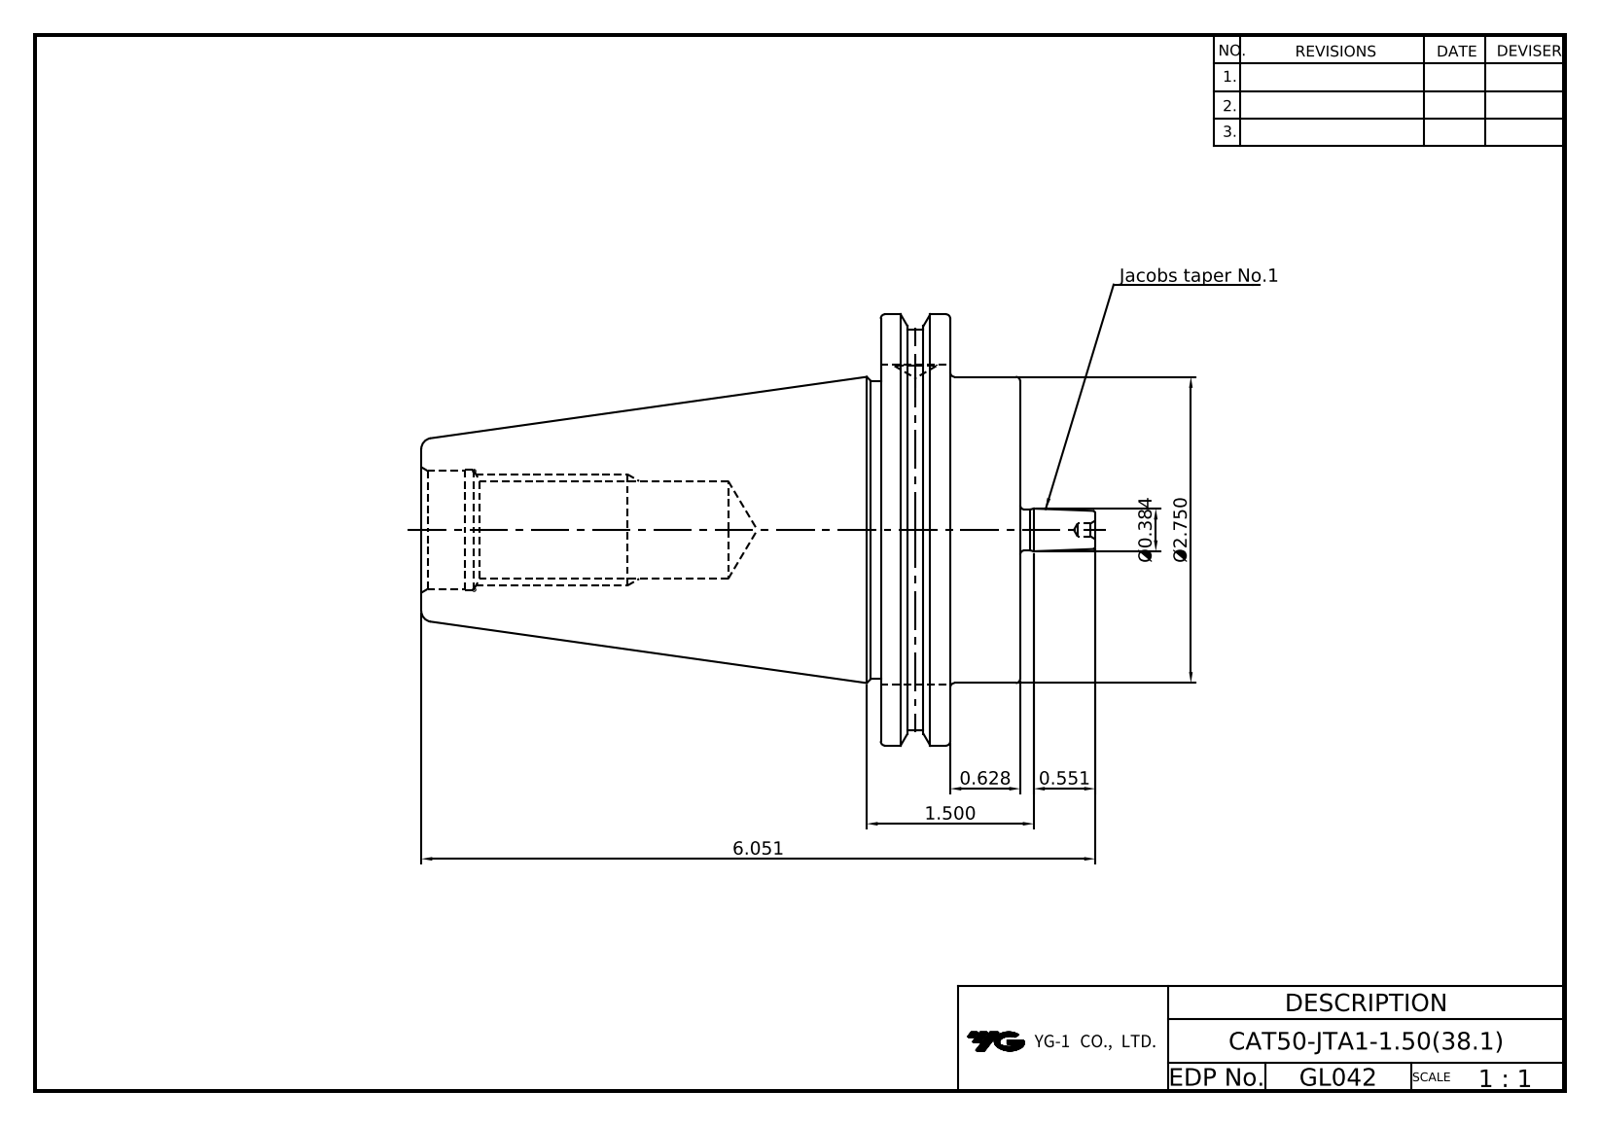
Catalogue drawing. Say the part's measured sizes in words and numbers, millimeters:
The part is named "CAT50-JTA1-1.50(20231109)". Its 3-D file was written by "Autodesk Inventor 2024 (AUTOMOTIVE_DESIGN)". It is 1 solid with 60 faces: 28 planar, 12 cylindrical and 20 other. Overall it measures 153.7 by 98.42 by 94.69 millimeters. Its volume is 399 395 cubic millimeters and its surface area 45 016 square millimeters. Round holes: 1 of diameter 9.53, 1 of diameter 21.97, 1 of diameter 26.2. Round bosses or shafts: 1 of diameter 98.42, 1 of diameter 91.29, 1 of diameter 69.85, 1 of diameter 69.25, 1 of diameter 9.3. The main face-to-face distances are 15.95, 15.88, 31.83, 104.77, 120.65, 136.6, 73.03, 25.9, 114.64, 9.87.
